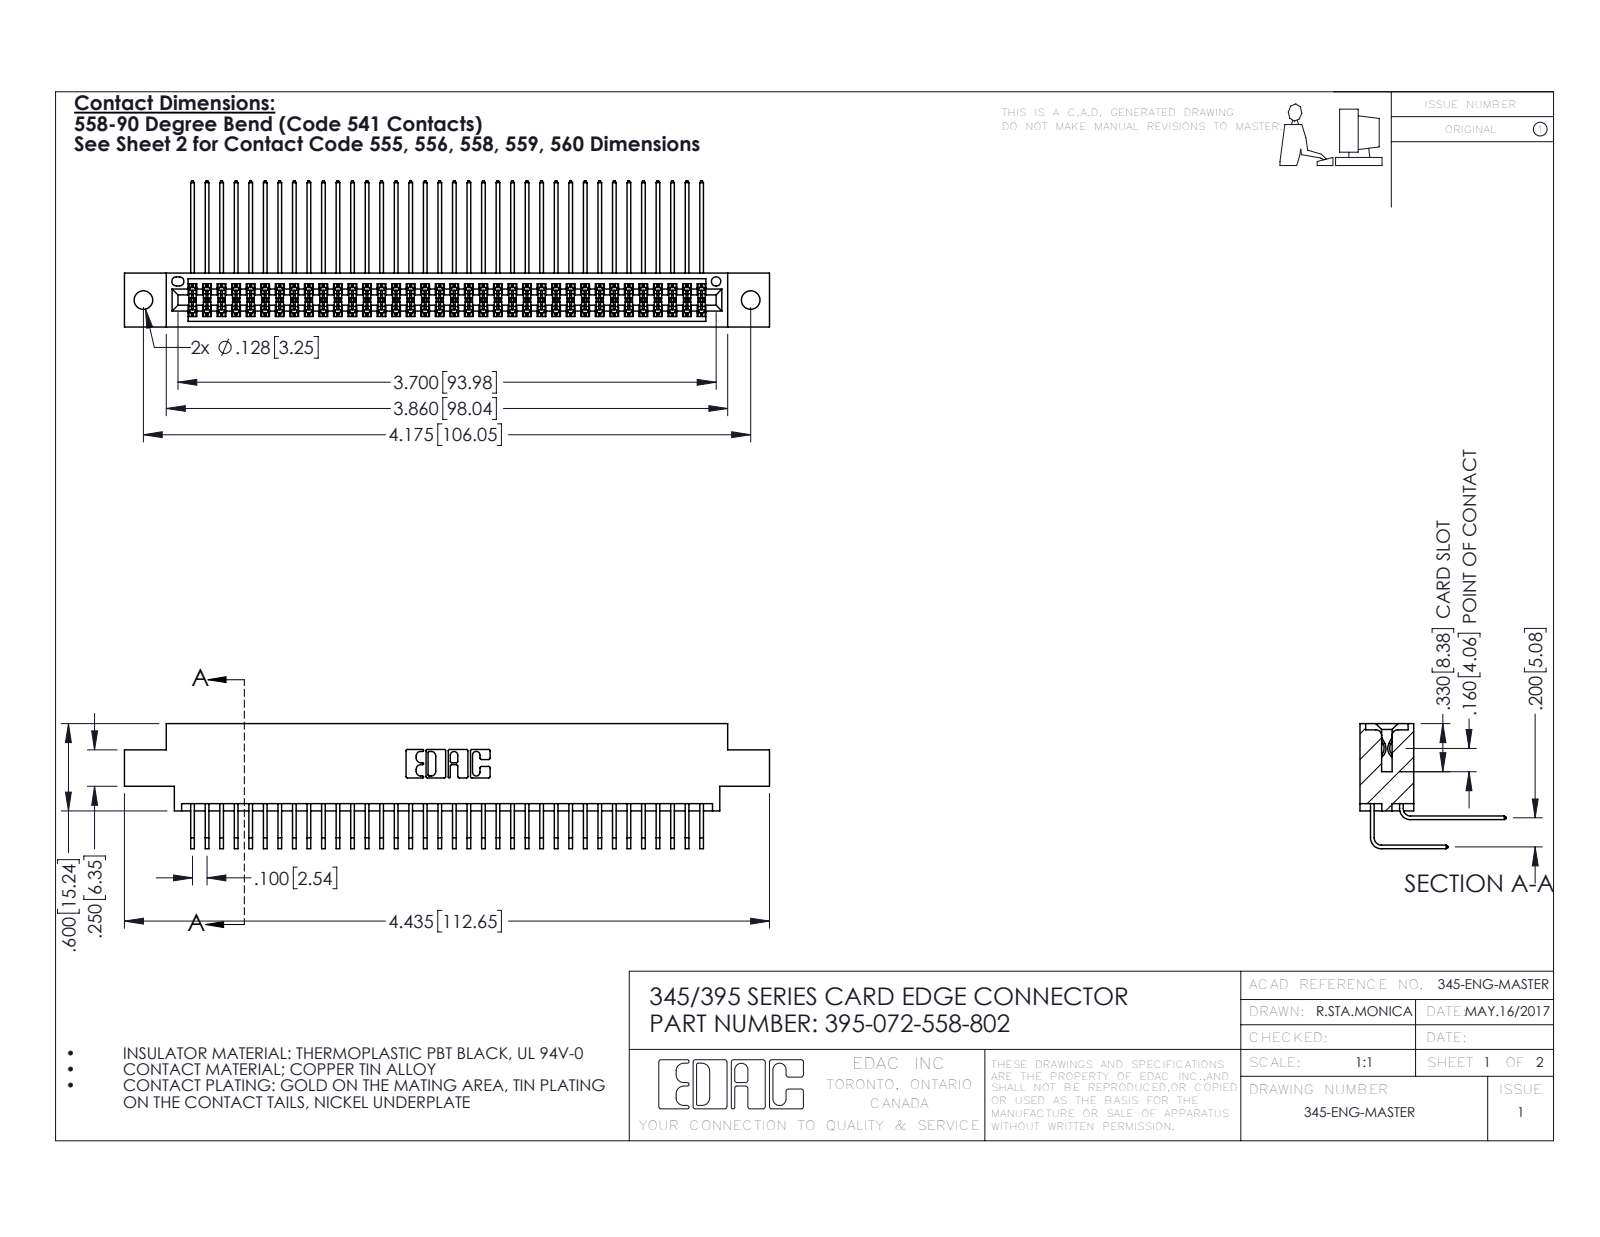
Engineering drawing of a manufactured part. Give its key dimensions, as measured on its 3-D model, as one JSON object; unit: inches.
{"part_name": "395-072-558-802; 345-292-001_558 Tail - 2; 345-292-001_558 559 Tail - 1; 345 Part_0.170 Offset - 0.128 Dia", "step_written_by": "SolidWorks 2016 (CONFIG_CONTROL_DESIGN)", "units": "inches", "bodies": {"solids": 73, "faces": 3874, "planar": 2604, "cylindrical": 1270, "other": 0}, "overall_size": [4.435, 1.005, 0.859], "volume_in3": 0.681, "surface_area_in2": 28.2, "round_holes": [[0.128, 2], [0.064, 1]], "partial_cylinders_radius": [[0.006, 108], [0.01, 22], [0.007, 6], [0.031, 6], [0.026, 3], [0.014, 2], [0.019, 2], [0.022, 2]], "face_to_face_distances": [0.072, 0.298, 0.2, 0.37, 0.098, 0.272, 0.025, 0.225, 0.175, 0.025], "hole_center_spacings": [0.27, 3.939, 4.175]}
